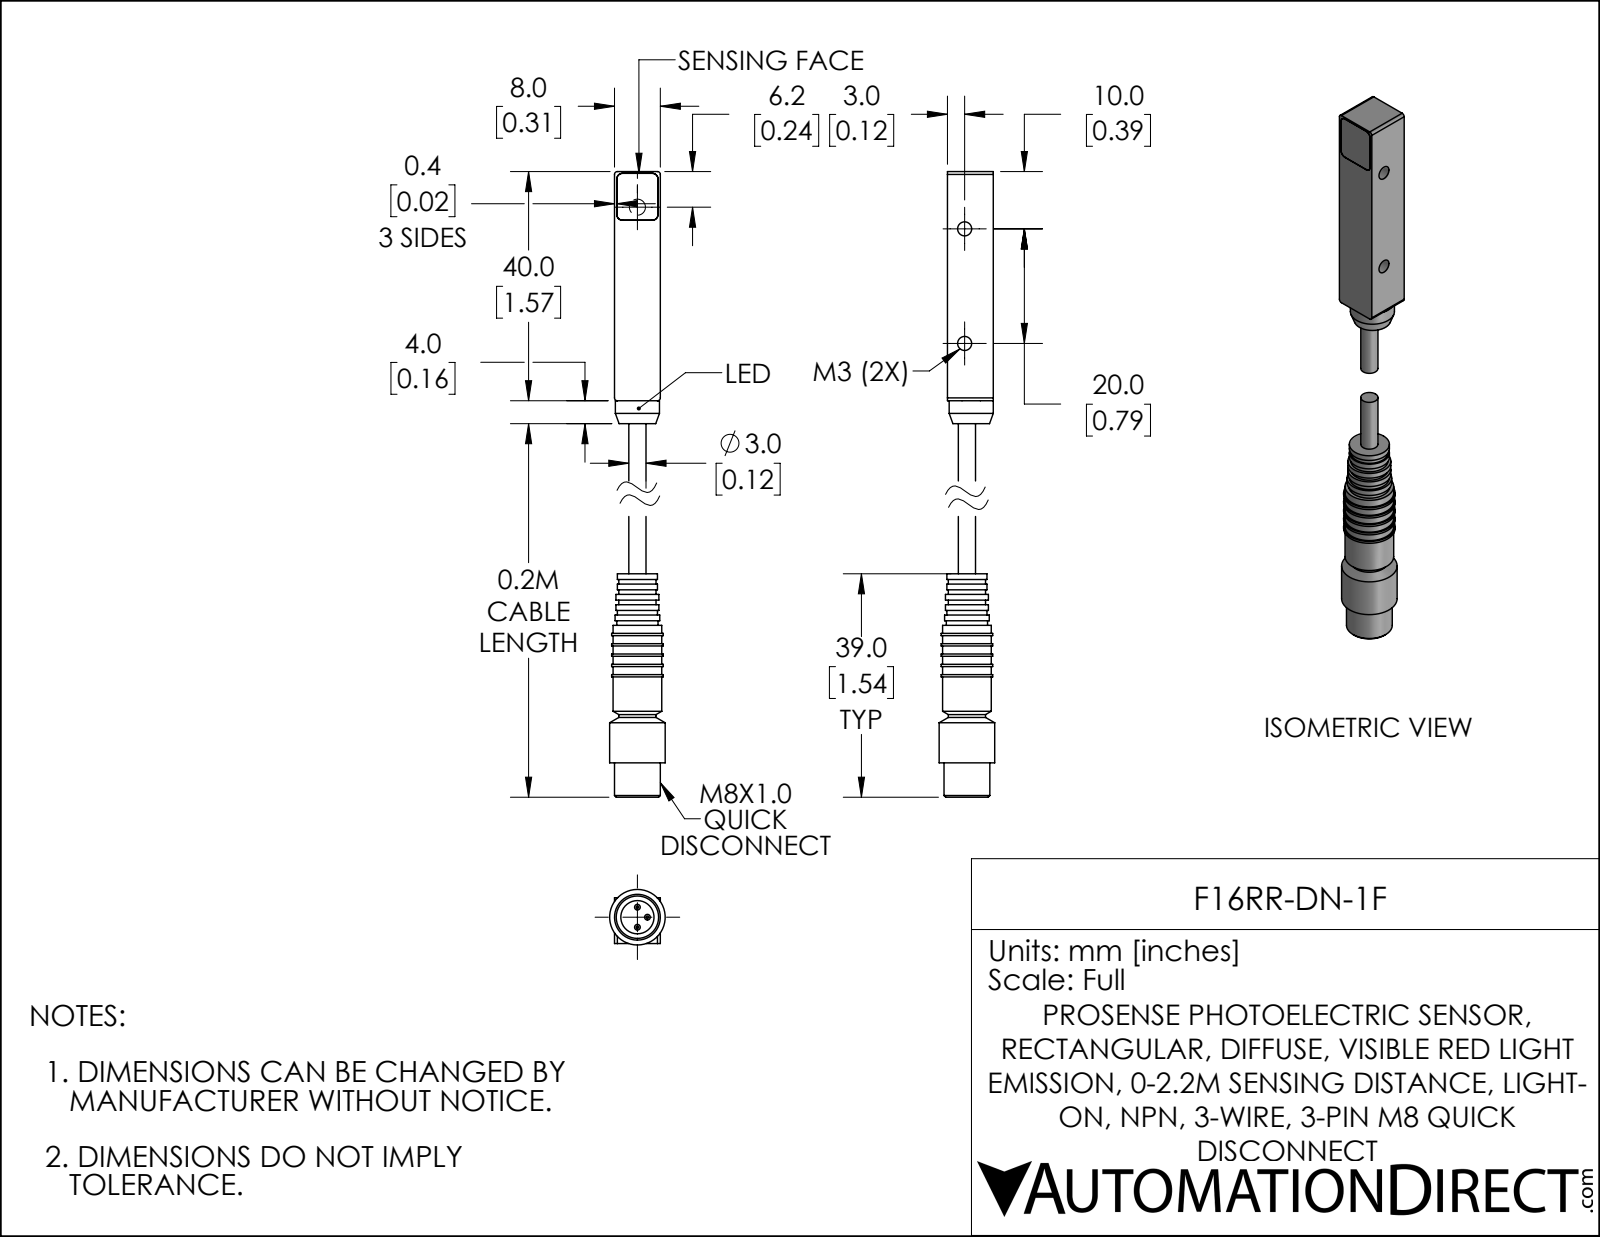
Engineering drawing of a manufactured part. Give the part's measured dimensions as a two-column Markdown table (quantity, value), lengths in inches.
| quantity | value |
| --- | --- |
| part name | F16RR-DN-1F_1; F16RR-DN-1F; F16RR-DN-1F_2 |
| STEP written by | SolidWorks 2019 (AUTOMOTIVE_DESIGN) |
| units | inches |
| bodies | 2 solids, 102 faces (50 planar, 45 cylindrical, 7 other) |
| overall size | 4.36 × 0.382 × 0.382 |
| volume | 0.293 in³ |
| surface area | 5.017 in² |
| round holes (diameter × count) | 0.097 × 2, 0.228 × 1 |
| round bosses / shafts (diameter × count) | 0.039 × 3, 0.382 × 1, 0.354 × 1, 0.335 × 1, 0.315 × 1, 0.307 × 1, 0.303 × 1, 0.295 × 1 |
| partial cylindrical surfaces (radius × count) | 0.02 × 4, 0.039 × 4, 0.039 × 4 |
| main face-to-face distances | 0.315, 0.071, 0.142, 0.039, 0.354, 1.732, 2.824, 2.431, 0.213, 1.092 |
| hole center spacings | 0.787 |
